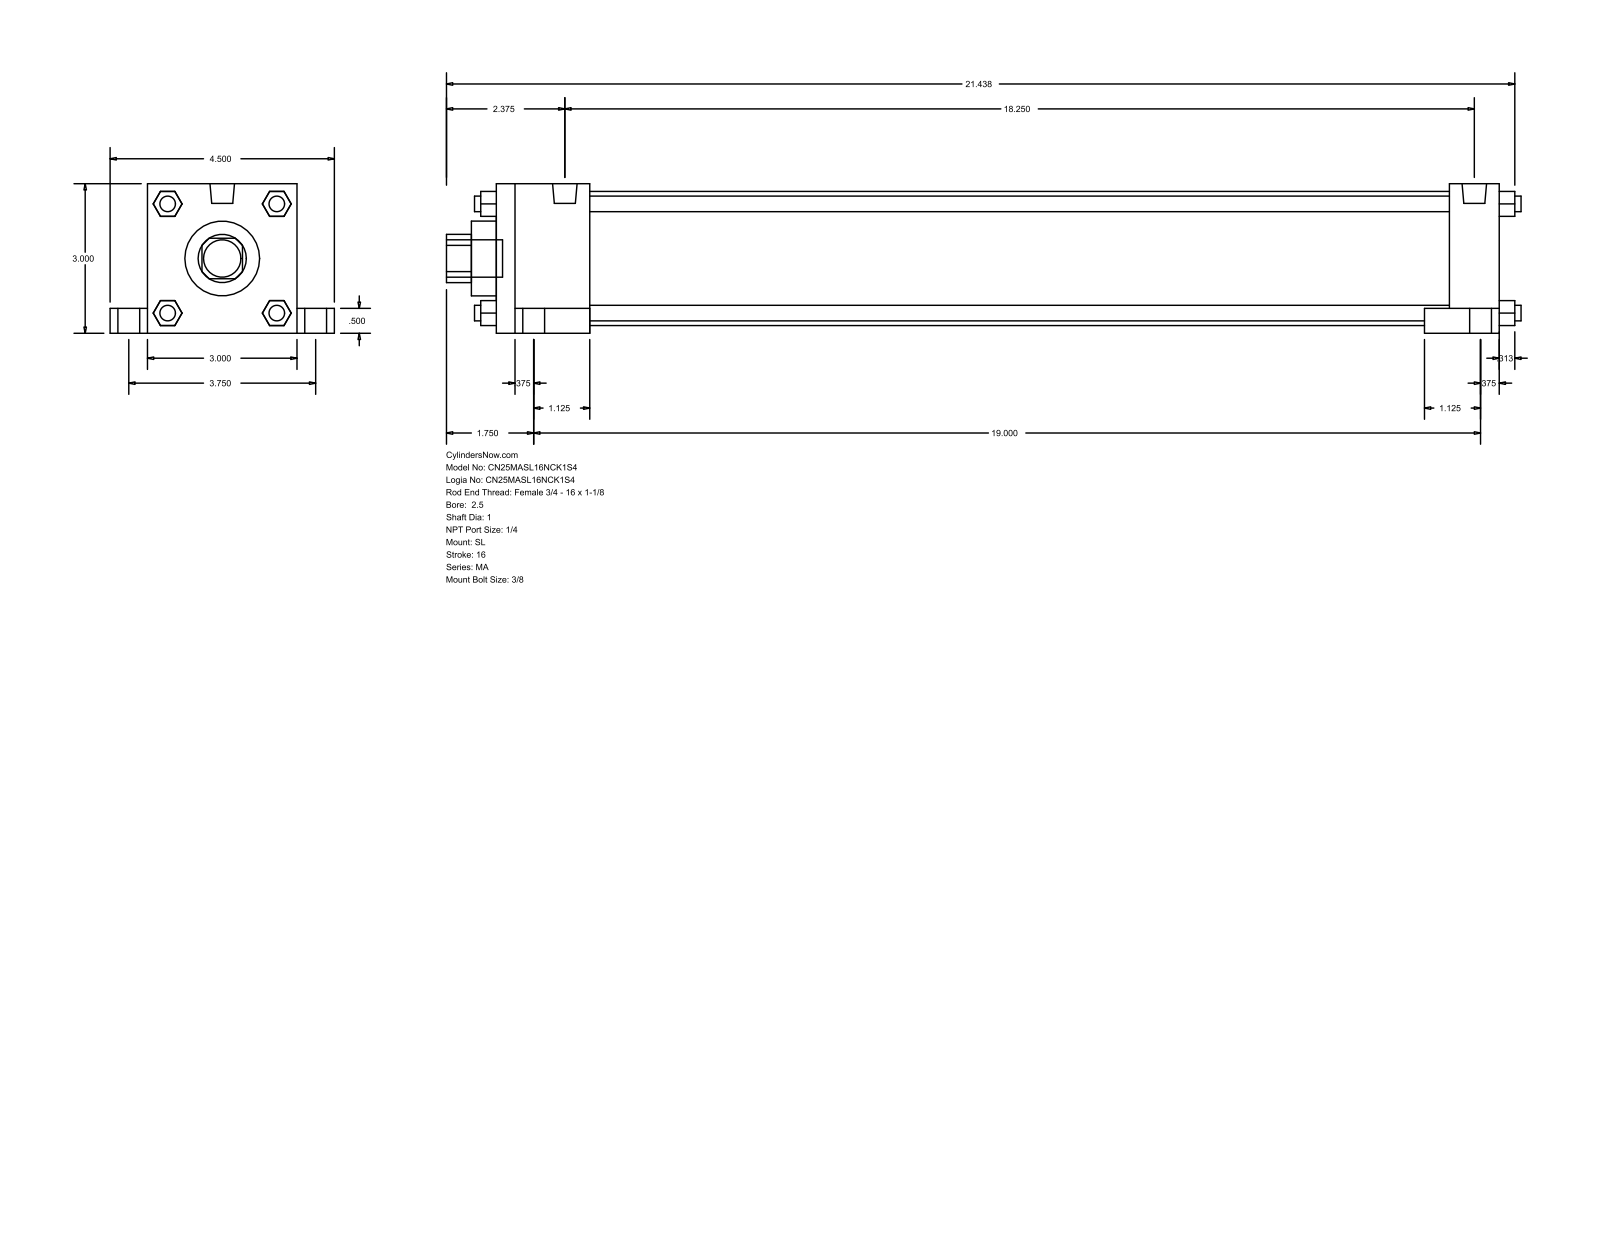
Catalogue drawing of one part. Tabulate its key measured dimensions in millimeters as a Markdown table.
| quantity | value |
| --- | --- |
| part name | MA_SL__0250_1 |
| STEP written by | GSSL Pune (CONFIG_CONTROL_DESIGN) |
| units | millimeters |
| bodies | 0 solids, 148 faces (112 planar, 36 cylindrical, 0 other) |
| overall size | 547.69 × 114.3 × 76.2 |
| round holes (diameter × count) | 25.4 × 1, 38.1 × 1, 68.33 × 1 |
| round bosses / shafts (diameter × count) | 7.94 × 8, 17.46 × 4, 11.11 × 4, 12.49 × 2, 19.05 × 1 |
| partial cylindrical surfaces (radius × count) | 12.29 × 1 |
| main face-to-face distances | 76.2, 511.18, 12.7, 438.15, 25.4, 47.63, 463.55, 485.78, 19.05, 95.25 |
